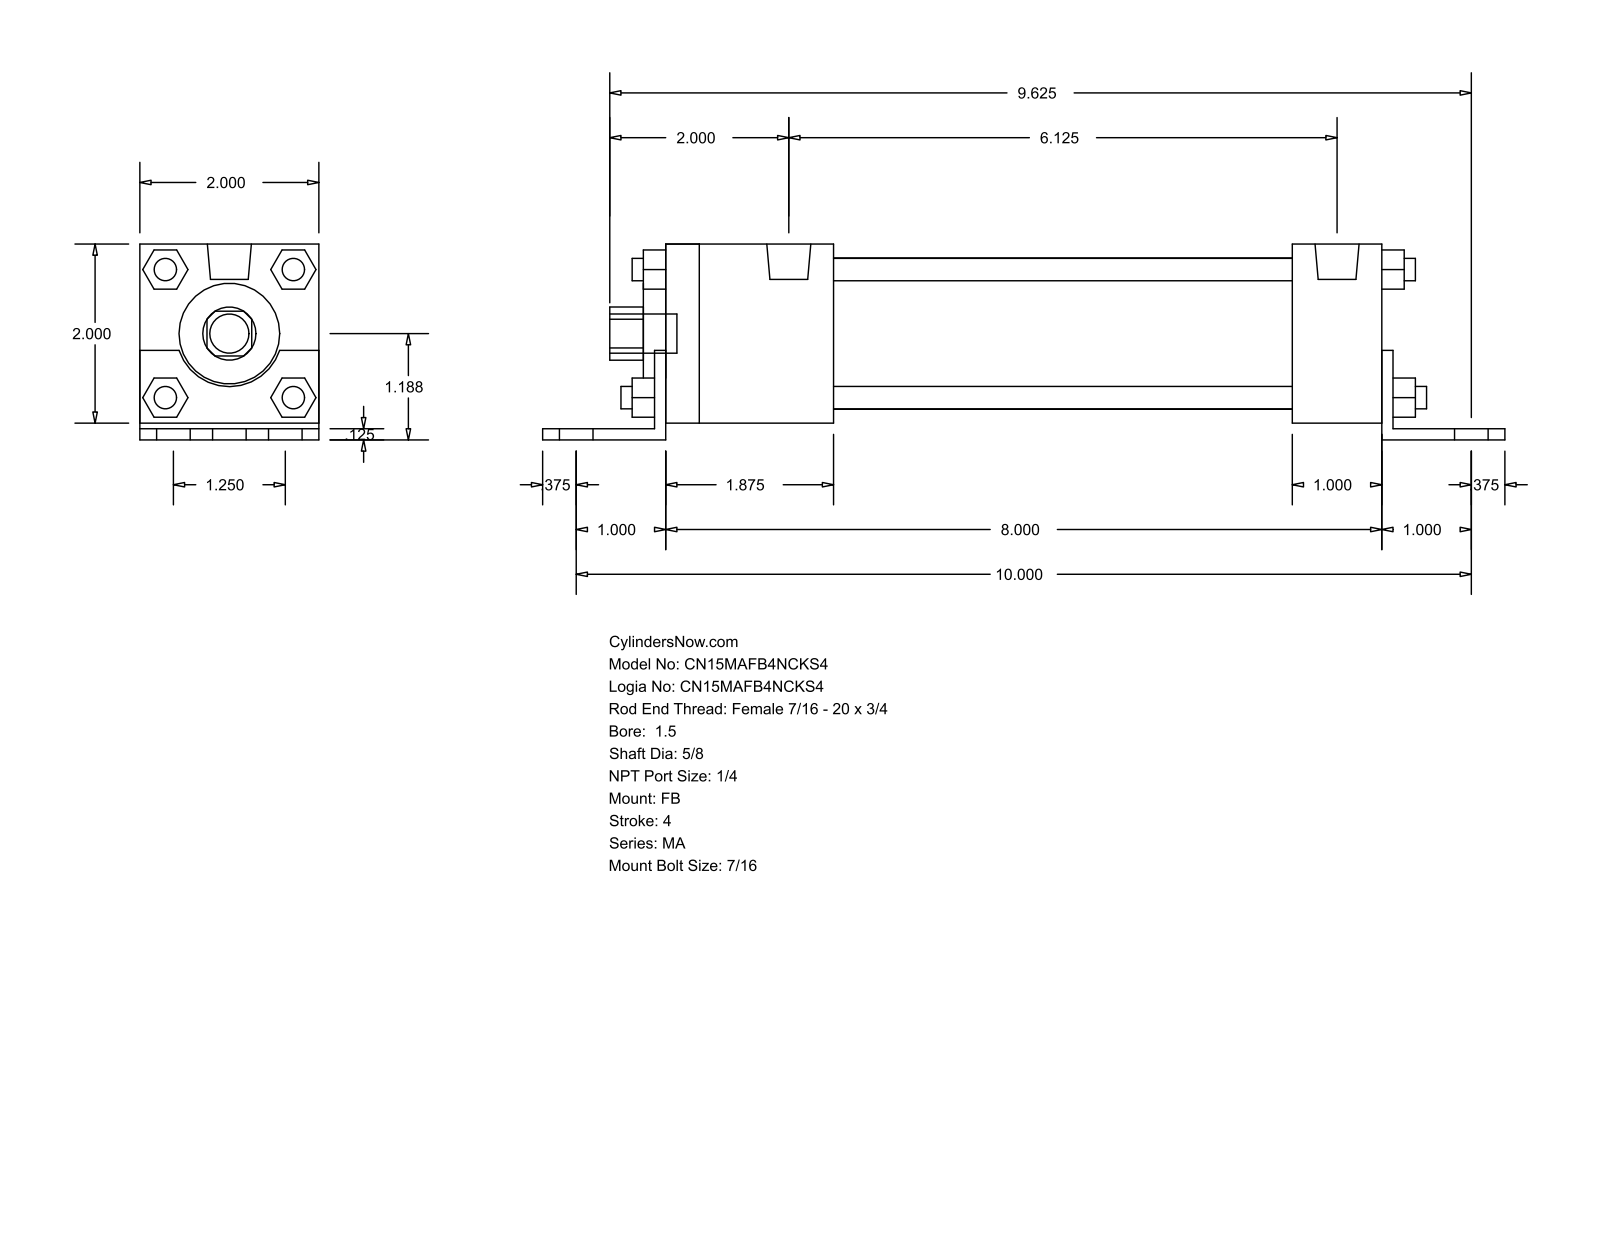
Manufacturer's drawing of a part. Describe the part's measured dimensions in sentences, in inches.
The part is named "MA_FB__0150_0.625". Its 3-D file was written by "GSSL Pune (CONFIG_CONTROL_DESIGN)". It is 0 solids with 140 faces: 105 planar, 35 cylindrical and 0 other. Overall it measures 10.75 by 2.187 by 2 inches. Round holes: 1 of diameter 0.625, 1 of diameter 1.125, 1 of diameter 1.69. Round bosses or shafts: 7 of diameter 0.437, 4 of diameter 0.313, 4 of diameter 0.25, 2 of diameter 0.492. Partial cylindrical surfaces (rounded edges, fillets, slot ends): 1 of radius 0.297, 1 of radius 0.593. The main face-to-face distances are 2, 0.125, 0.187, 2.187, 0.063, 2.063, 0.125, 8.125, 0.25, 8.
